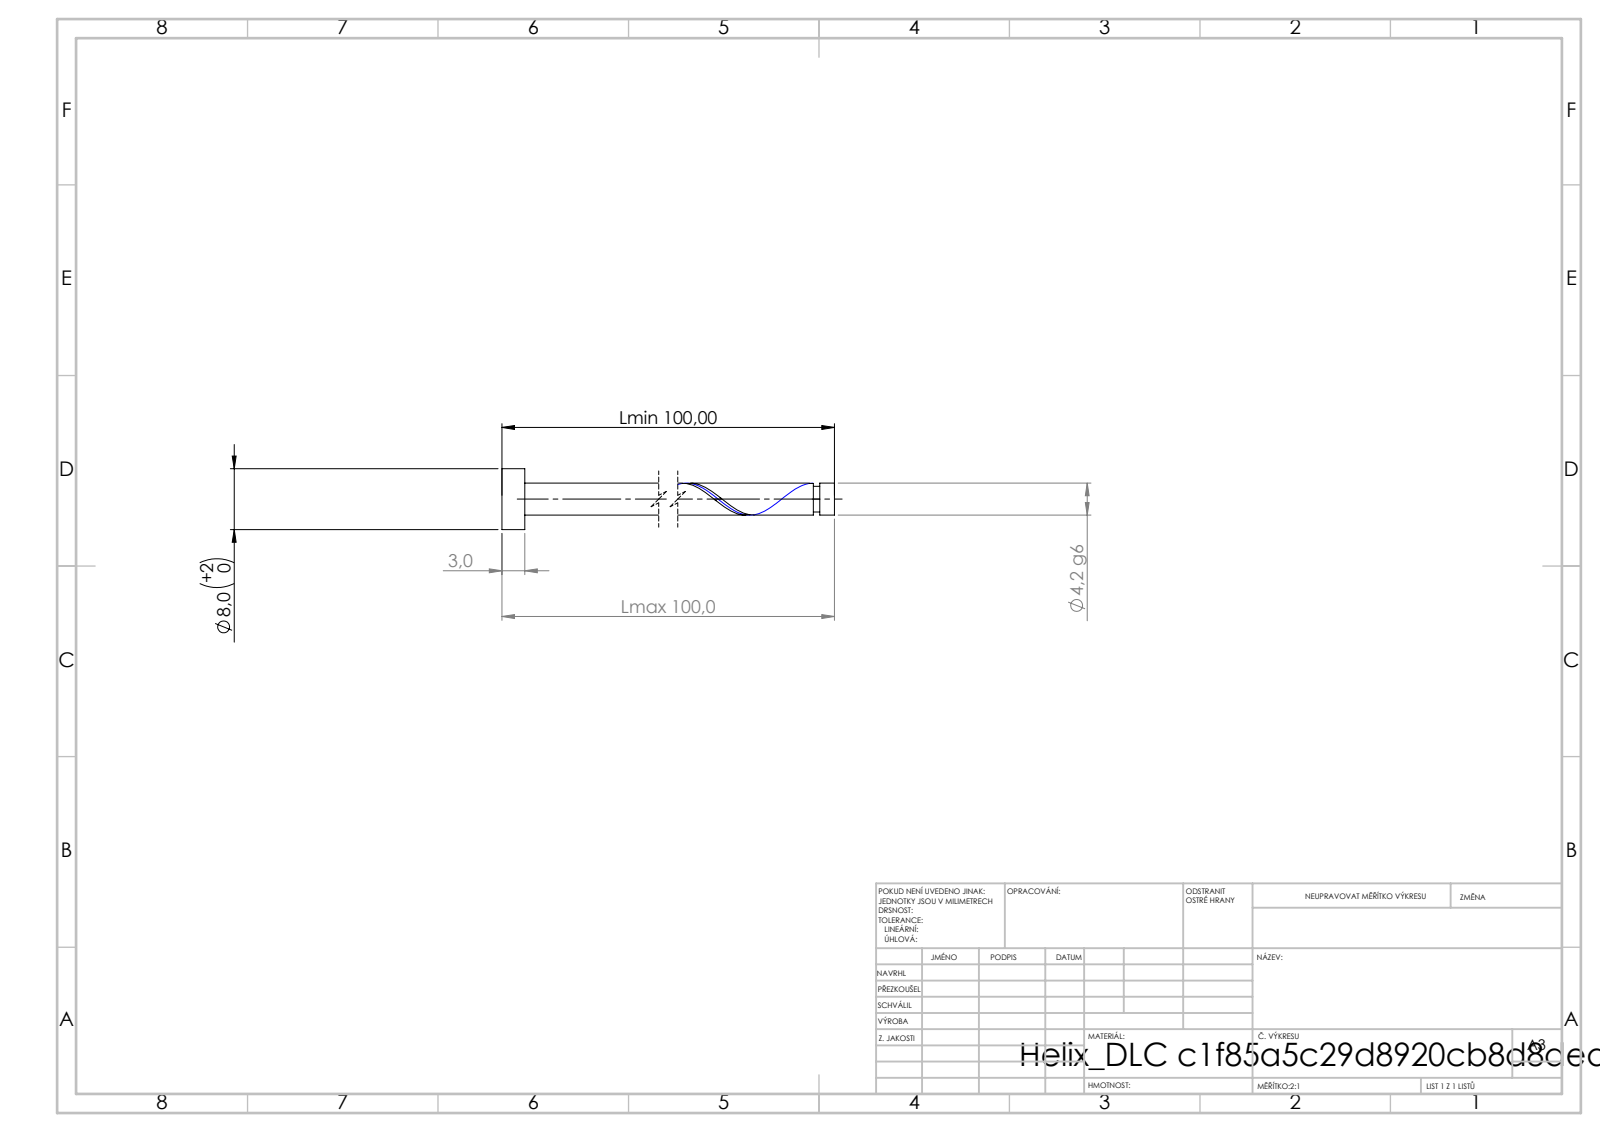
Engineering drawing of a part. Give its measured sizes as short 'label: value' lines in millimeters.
written by: SolidWorks 2019 (CONFIG_CONTROL_DESIGN)
unit: mm
bodies: 1 solid, 21 faces (6 planar, 14 cylindrical, 1 other)
size: 100 × 8 × 8
volume: 1 477 mm³; area: 1 491 mm²
bosses: 1× ⌀8, 1× ⌀4.2, 1× ⌀3.36
face distances: 3, 100, 97, 98.07, 95.07, 1.93, 97.23, 94.23, 0.84, 2.77
